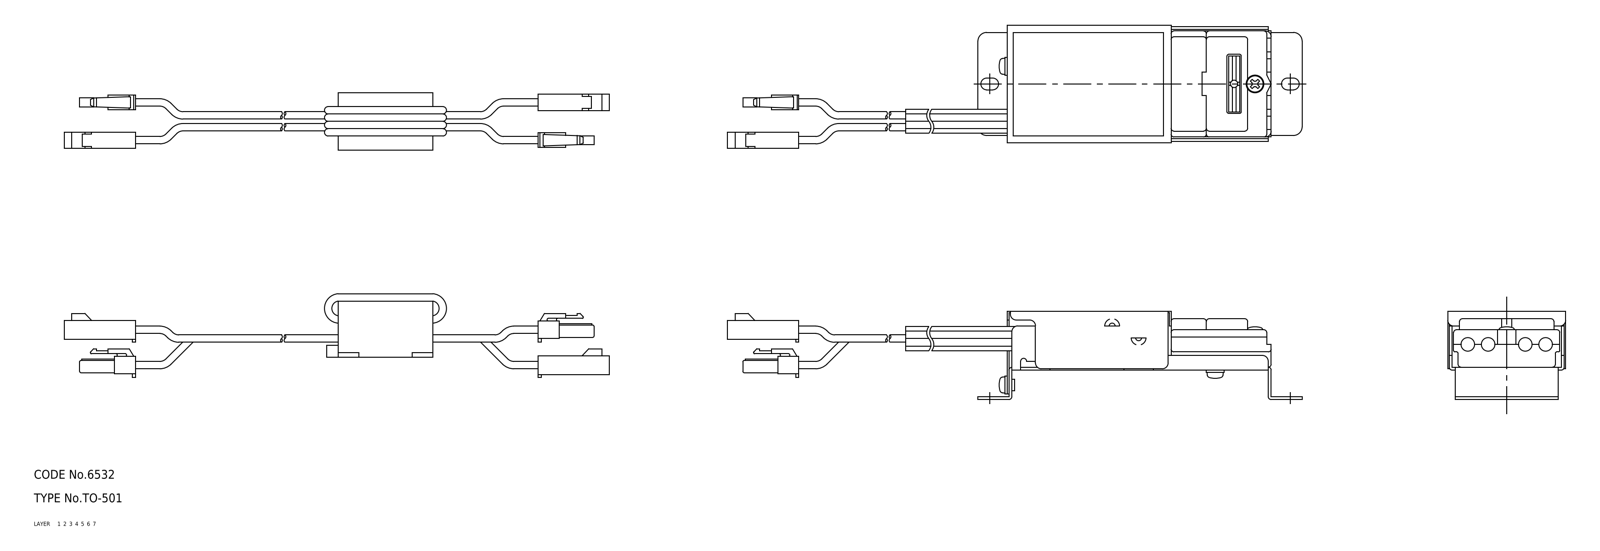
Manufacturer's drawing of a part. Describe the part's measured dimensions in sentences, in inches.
The part is named "67145058; 67145071; 67145084; 67145097 (+8 more)". Its 3-D file was written by "CADfix (AUTOMOTIVE_DESIGN)". It is 17 solids with 788 faces: 0 planar, 0 cylindrical and 788 other. Overall it measures 17.232 by 1.821 by 1.294 inches. Its volume is 2.526 cubic inches and its surface area 70.78 square inches.
